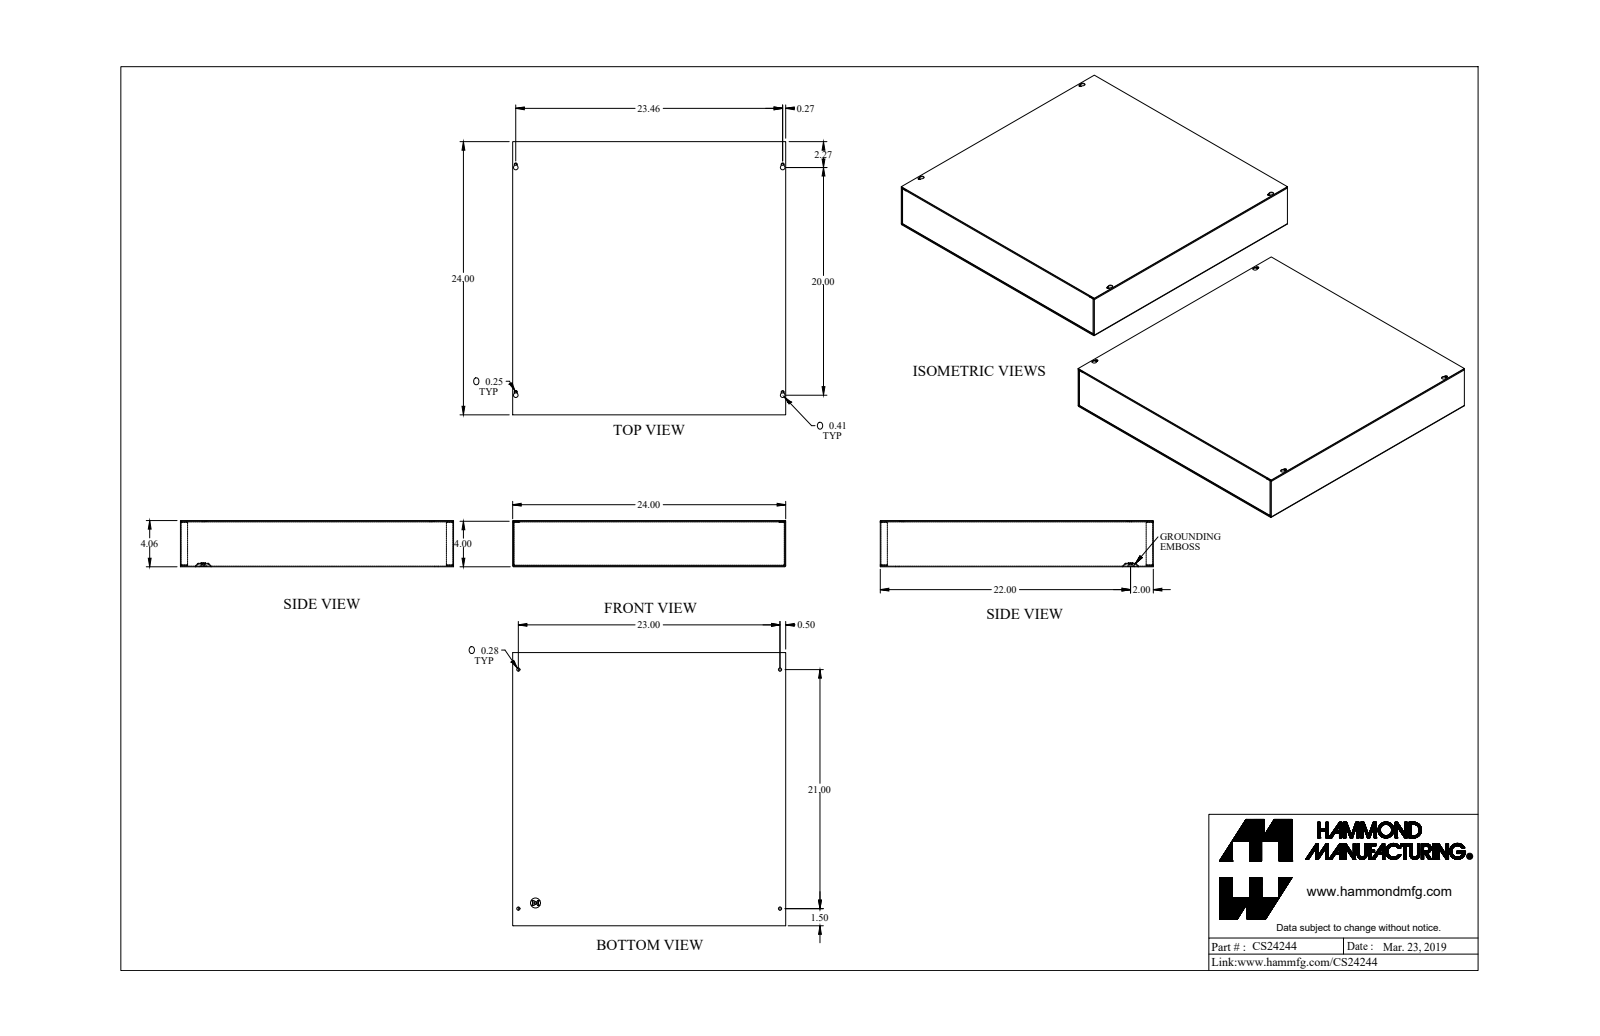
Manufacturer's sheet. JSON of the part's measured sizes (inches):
{"part_name": "CS24244_Default", "step_written_by": "SolidWorks 2019 (CONFIG_CONTROL_DESIGN)", "units": "inches", "bodies": {"solids": 4, "faces": 205, "planar": 125, "cylindrical": 72, "other": 8}, "overall_size": [24, 24, 4.057], "volume_in3": 91.16, "surface_area_in2": 3218, "round_holes": [[0.17, 5], [0.281, 4], [0.5, 1]], "round_bosses_or_shafts": [[0.492, 1], [0.284, 1]], "partial_cylinders_radius": [[0.029, 12], [0.086, 12], [0.057, 8], [0.125, 4], [0.203, 4]], "face_to_face_distances": [0.057, 4, 3.943, 4.057, 23.943, 24, 23.886, 0.08, 3.863, 3.92], "hole_center_spacings": [0.55, 20.501, 23.235, 30.982, 20, 21, 23, 23.46]}
